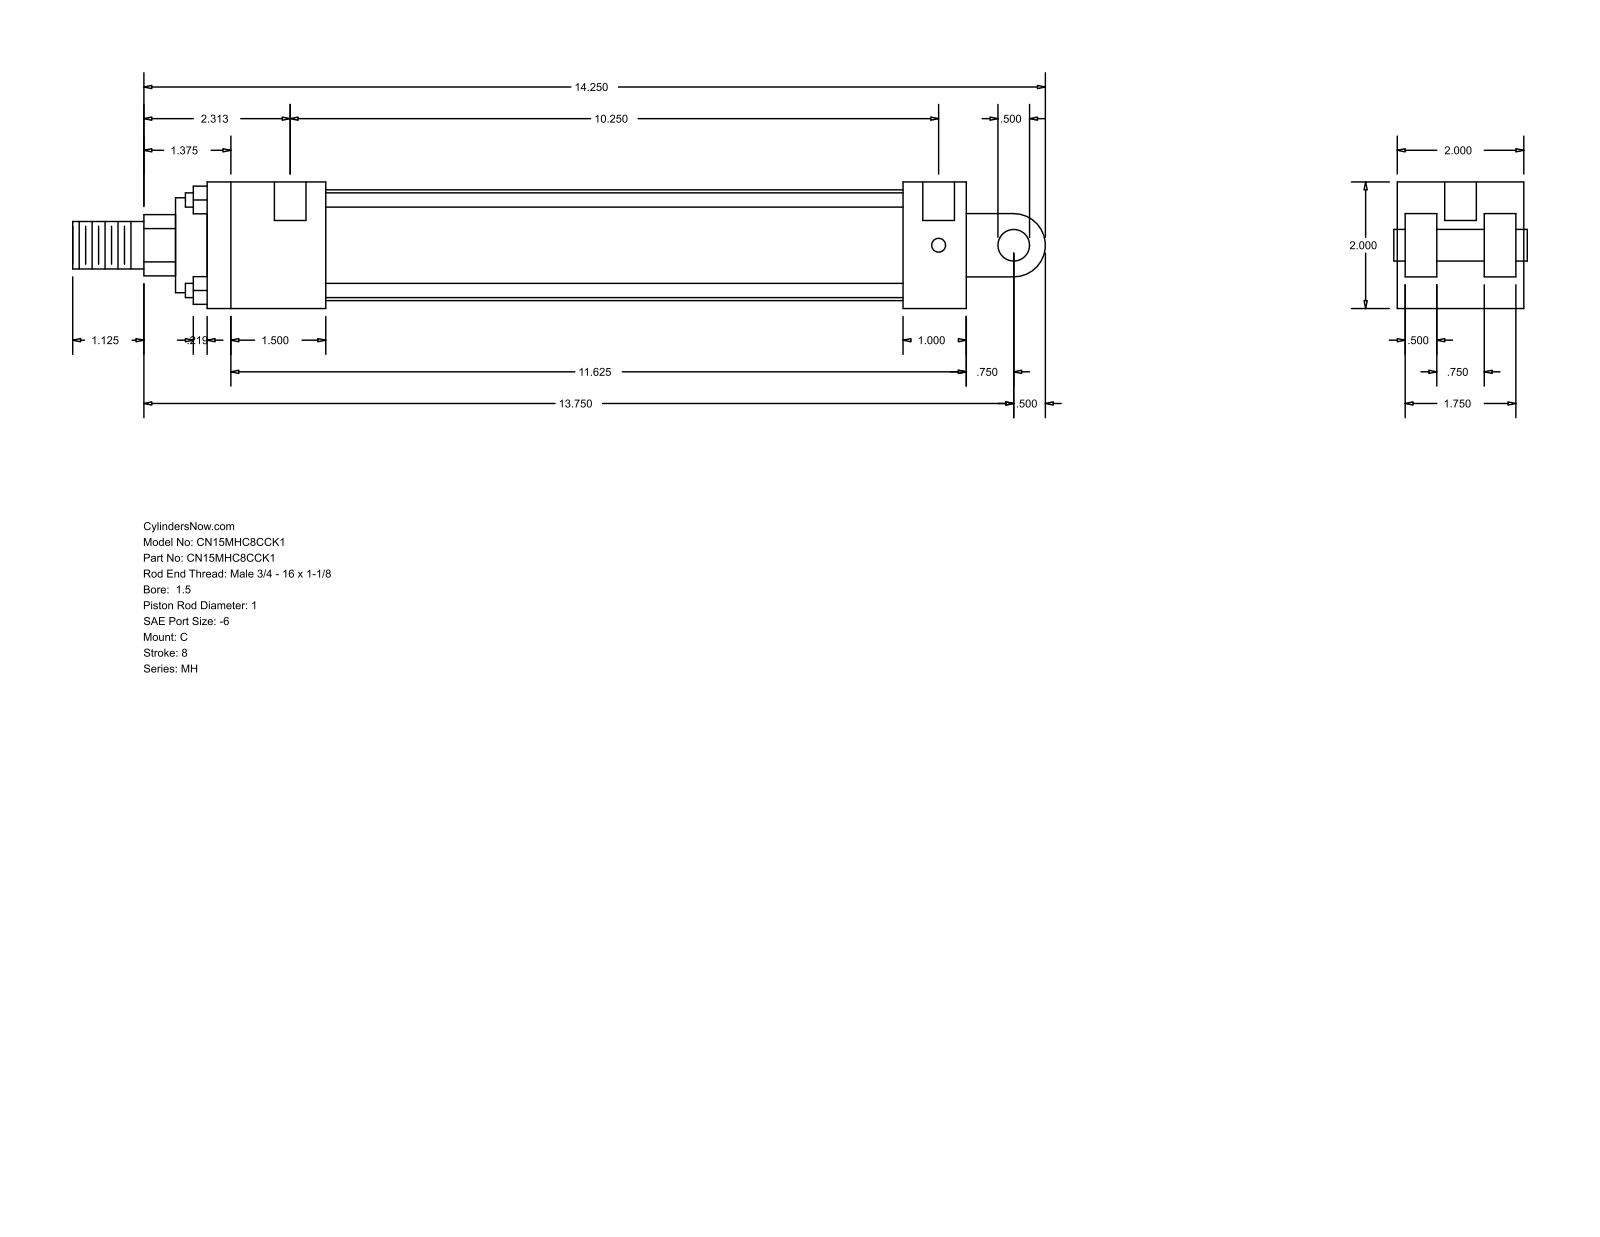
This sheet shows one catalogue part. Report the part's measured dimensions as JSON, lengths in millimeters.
{"part_name": "MH_C__0150_1", "step_written_by": "GSSL Pune (CONFIG_CONTROL_DESIGN)", "units": "millimeters", "bodies": {"solids": 0, "faces": 99, "planar": 70, "cylindrical": 29, "other": 0}, "overall_size": [390.52, 50.8, 50.8], "round_holes": [[5.56, 4], [12.7, 2]], "round_bosses_or_shafts": [[5.71, 4], [44.45, 1], [38.1, 1], [25.4, 1], [19.05, 1], [12.7, 1]], "partial_cylinders_radius": [[12.29, 1], [12.7, 1]], "face_to_face_distances": [50.8, 12.7, 47.63, 25.4, 3.17, 15.87, 34.93, 31.76, 304.8, 38.1], "hole_center_spacings": [263.53, 3.18, 260.35]}
